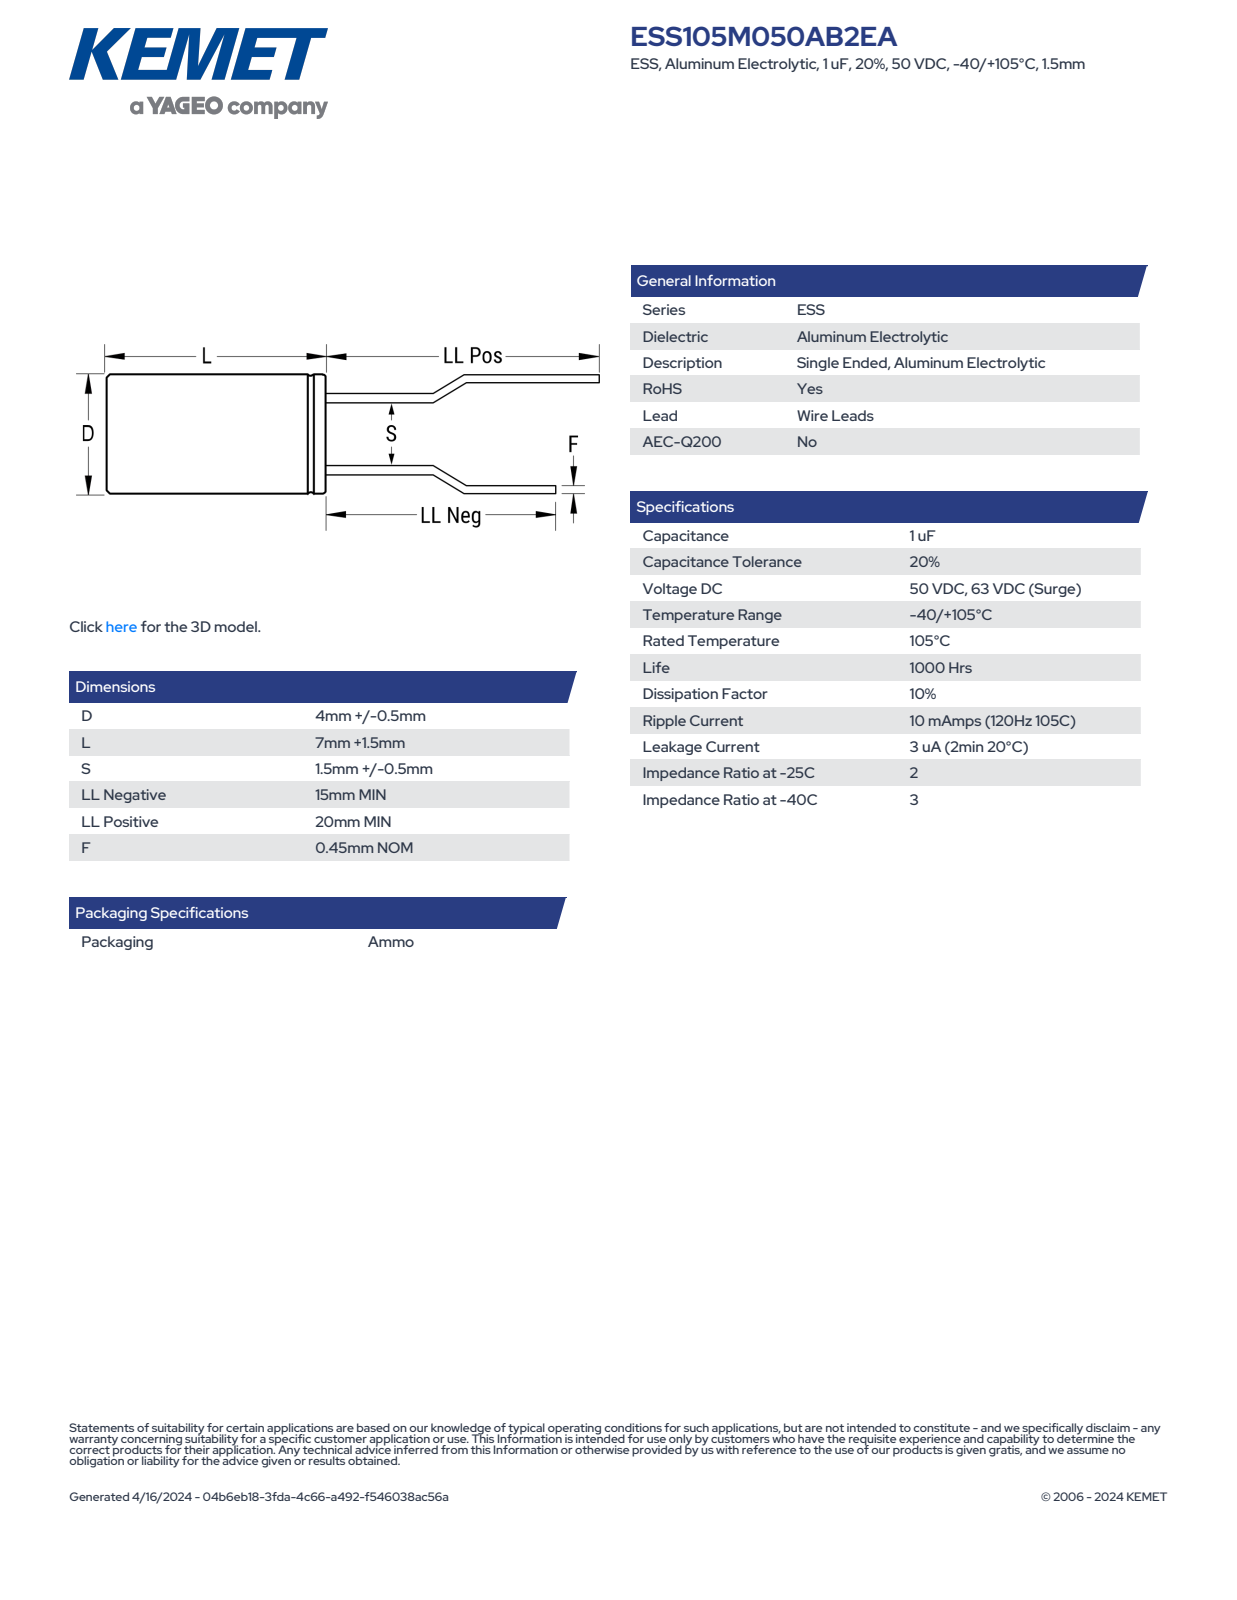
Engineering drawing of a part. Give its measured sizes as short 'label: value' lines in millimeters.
name: CAR_KTRS_4X7_D4.5L8.5S1.5F0.45
written by: SolidWorks 2021 (AUTOMOTIVE_DESIGN)
unit: mm
bodies: 4 solids, 73 faces (61 planar, 8 cylindrical, 4 other)
size: 28.5 × 4.5 × 4.5
volume: 140 mm³; area: 206 mm²
bosses: 2× ⌀0.45, 1× ⌀4.5
face distances: 8.5, 8.51, 23.51, 28.51, 23.5, 28.5, 15, 20, 5, 0.54
